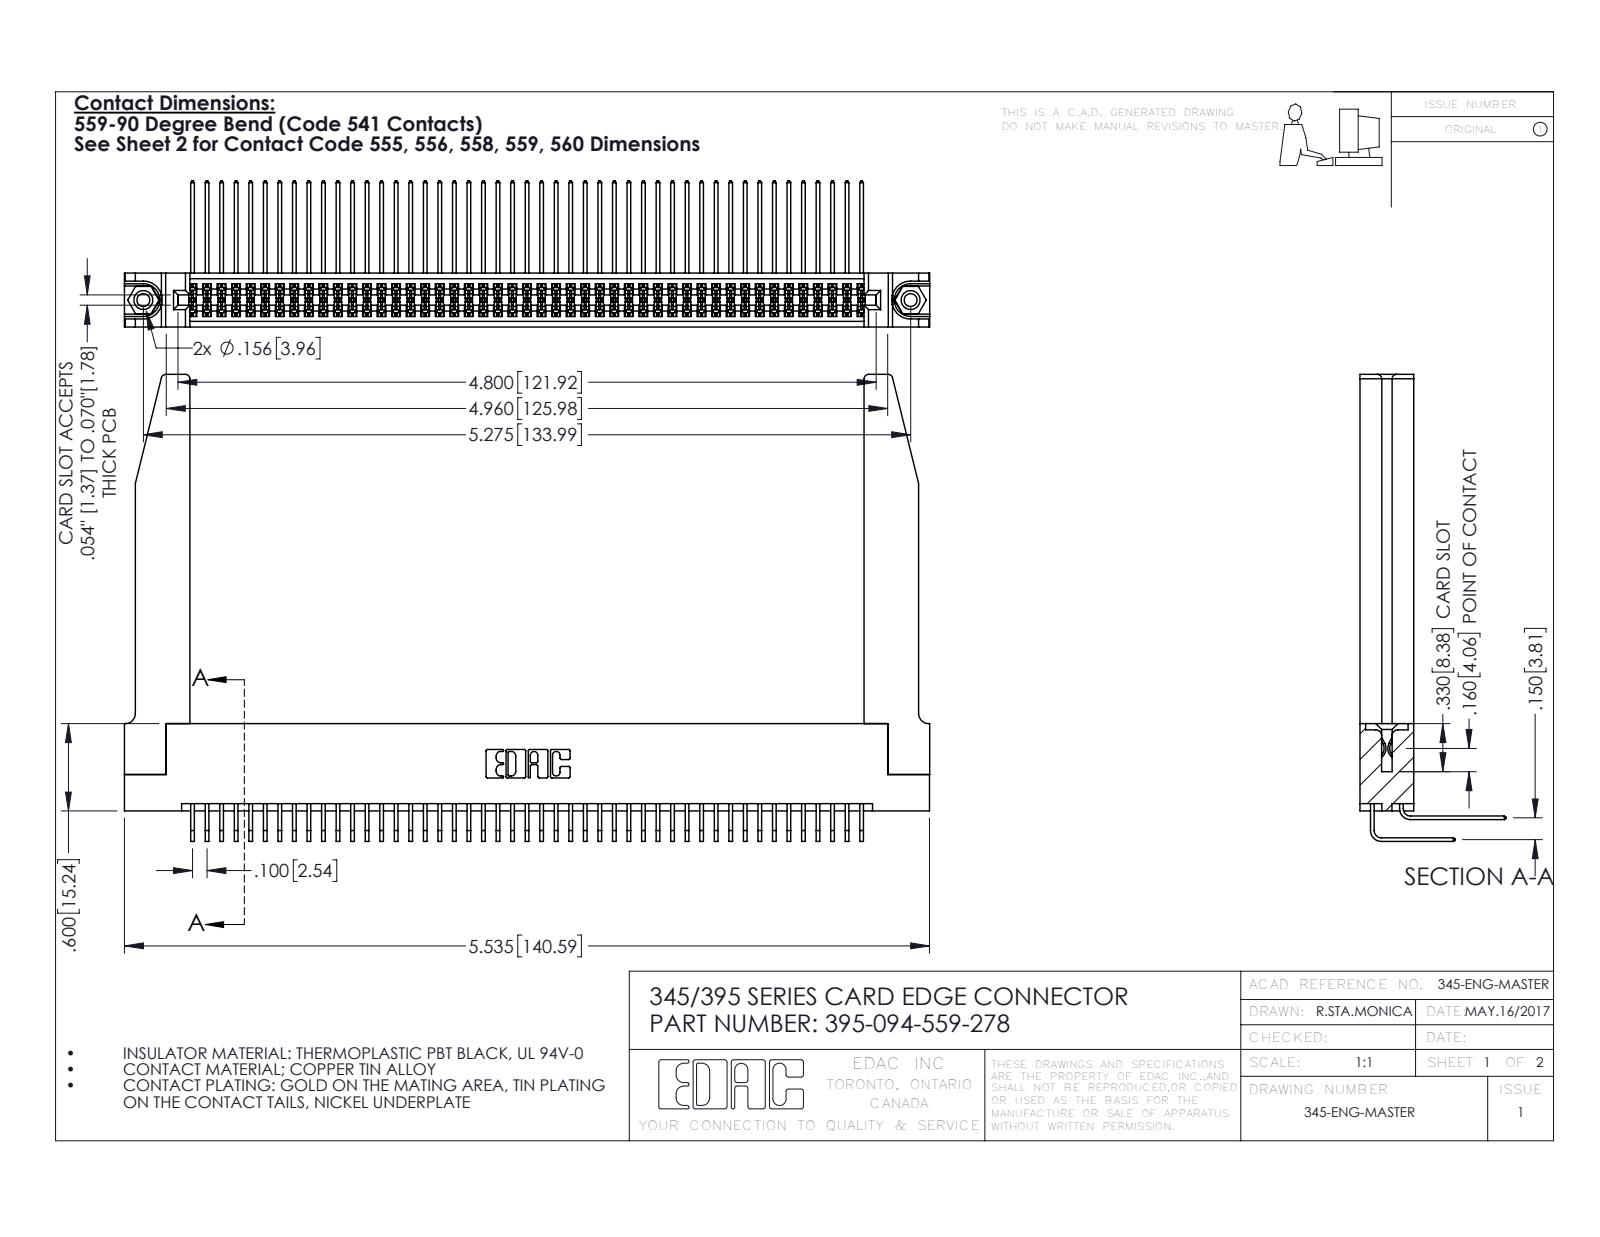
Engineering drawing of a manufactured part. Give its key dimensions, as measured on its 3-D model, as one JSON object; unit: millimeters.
{"part_name": "345-292-001_558 559 Tail - 1; 395-094-559-278; 345 Part_Flush Mounting Lugs - 0.156 Dia-TH; 345-220-078_345-220-078 (+2 more)", "step_written_by": "SolidWorks 2016 (CONFIG_CONTROL_DESIGN)", "units": "millimeters", "bodies": {"solids": 99, "faces": 5248, "planar": 3512, "cylindrical": 1684, "other": 52}, "overall_size": [140.6, 81.5, 25.5], "volume_mm3": 22020, "surface_area_mm2": 30550, "round_holes": [[2.3, 2], [3.2, 2], [4, 2], [1.6, 1]], "round_bosses_or_shafts": [[3.9, 2]], "partial_cylinders_radius": [[0.2, 141], [0.3, 22], [0.8, 8], [0.2, 6], [0.8, 6], [0.7, 3], [0.4, 2], [0.5, 2]], "face_to_face_distances": [1.8, 9.4, 7.6, 5.1, 2.5, 6.9, 0.6, 5.7, 4.4, 3.8], "hole_center_spacings": [6.9, 128, 134]}
